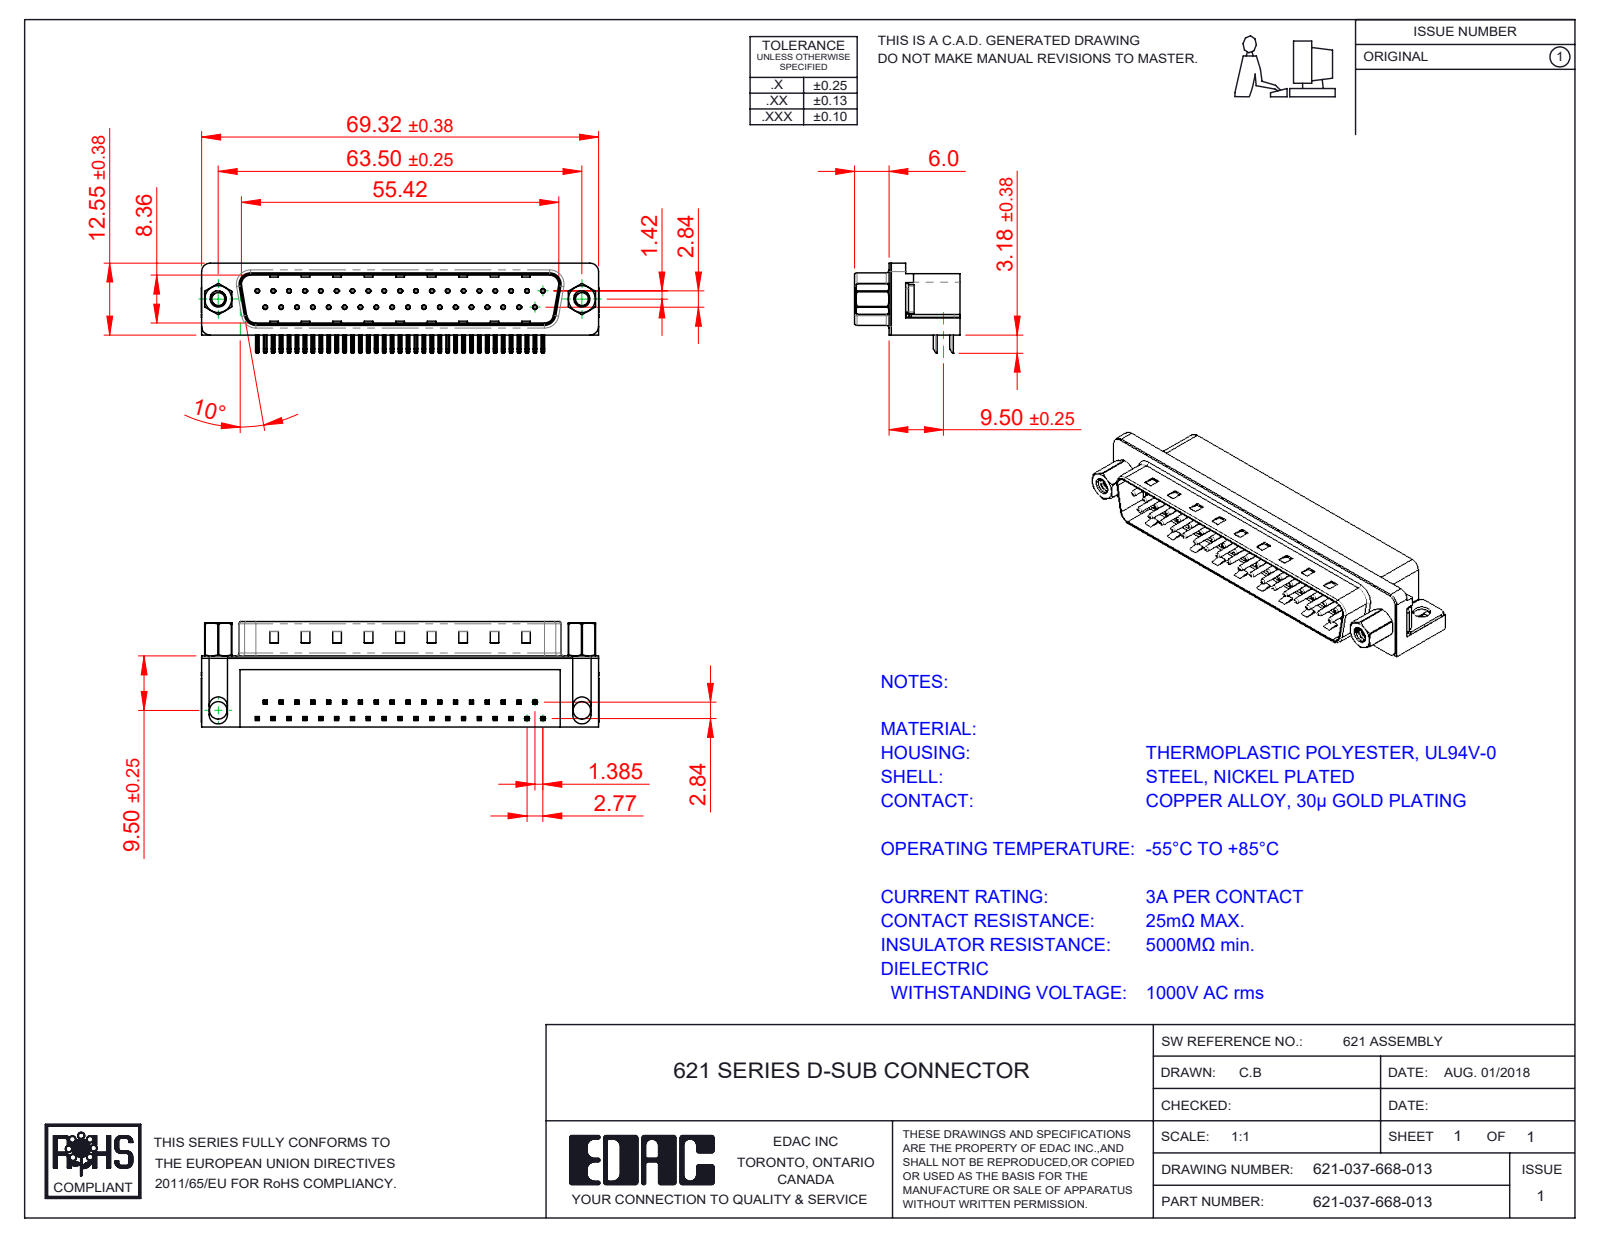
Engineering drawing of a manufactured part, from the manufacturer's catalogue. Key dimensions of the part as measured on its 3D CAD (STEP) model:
Part name (STEP PRODUCT): 621-037-668-013; 621 Housing_37 Socket; 621 Thru Hole Board Mount; 621 4-40 Hex Standoff 5 (+4 more)
STEP written by: SolidWorks 2016 (CONFIG_CONTROL_DESIGN)
Units: millimetres
Bodies: 45 solids, 3323 faces (2033 planar, 987 cylindrical, 303 other)
Overall size (bounding box): 69.4 × 18.4 × 15.73
Volume: 8 832 mm³ · Surface area: 10 564 mm²
Round holes (diameter × count): ⌀0.35 ×37, ⌀0.8 ×37, ⌀2.26 ×2, ⌀2.29 ×2, ⌀3.05 ×2, ⌀4 ×2, ⌀4.8 ×2, ⌀5 ×2
Round bosses / shafts (diameter × count): ⌀0.75 ×37, ⌀4.9 ×2, ⌀4.75 ×2, ⌀3.9 ×2, ⌀2.79 ×2
Partial cylindrical surfaces — rounded edges, fillets, slot ends (radius × count): R0.25 ×156, R0.12 ×74, R1 ×16, R0.5 ×9, R1.6 ×8, R1.5 ×7, R0.9 ×4, R2 ×4
Main face-to-face distances: 0.4, 12, 10.35, 8.76, 2.1, 1.7, 10.46, 10.86, 12.4, 9
Hole centre spacings: 3.16, 2.77, 5.54, 8.31, 11.08, 13.85, 19.39, 22.16
